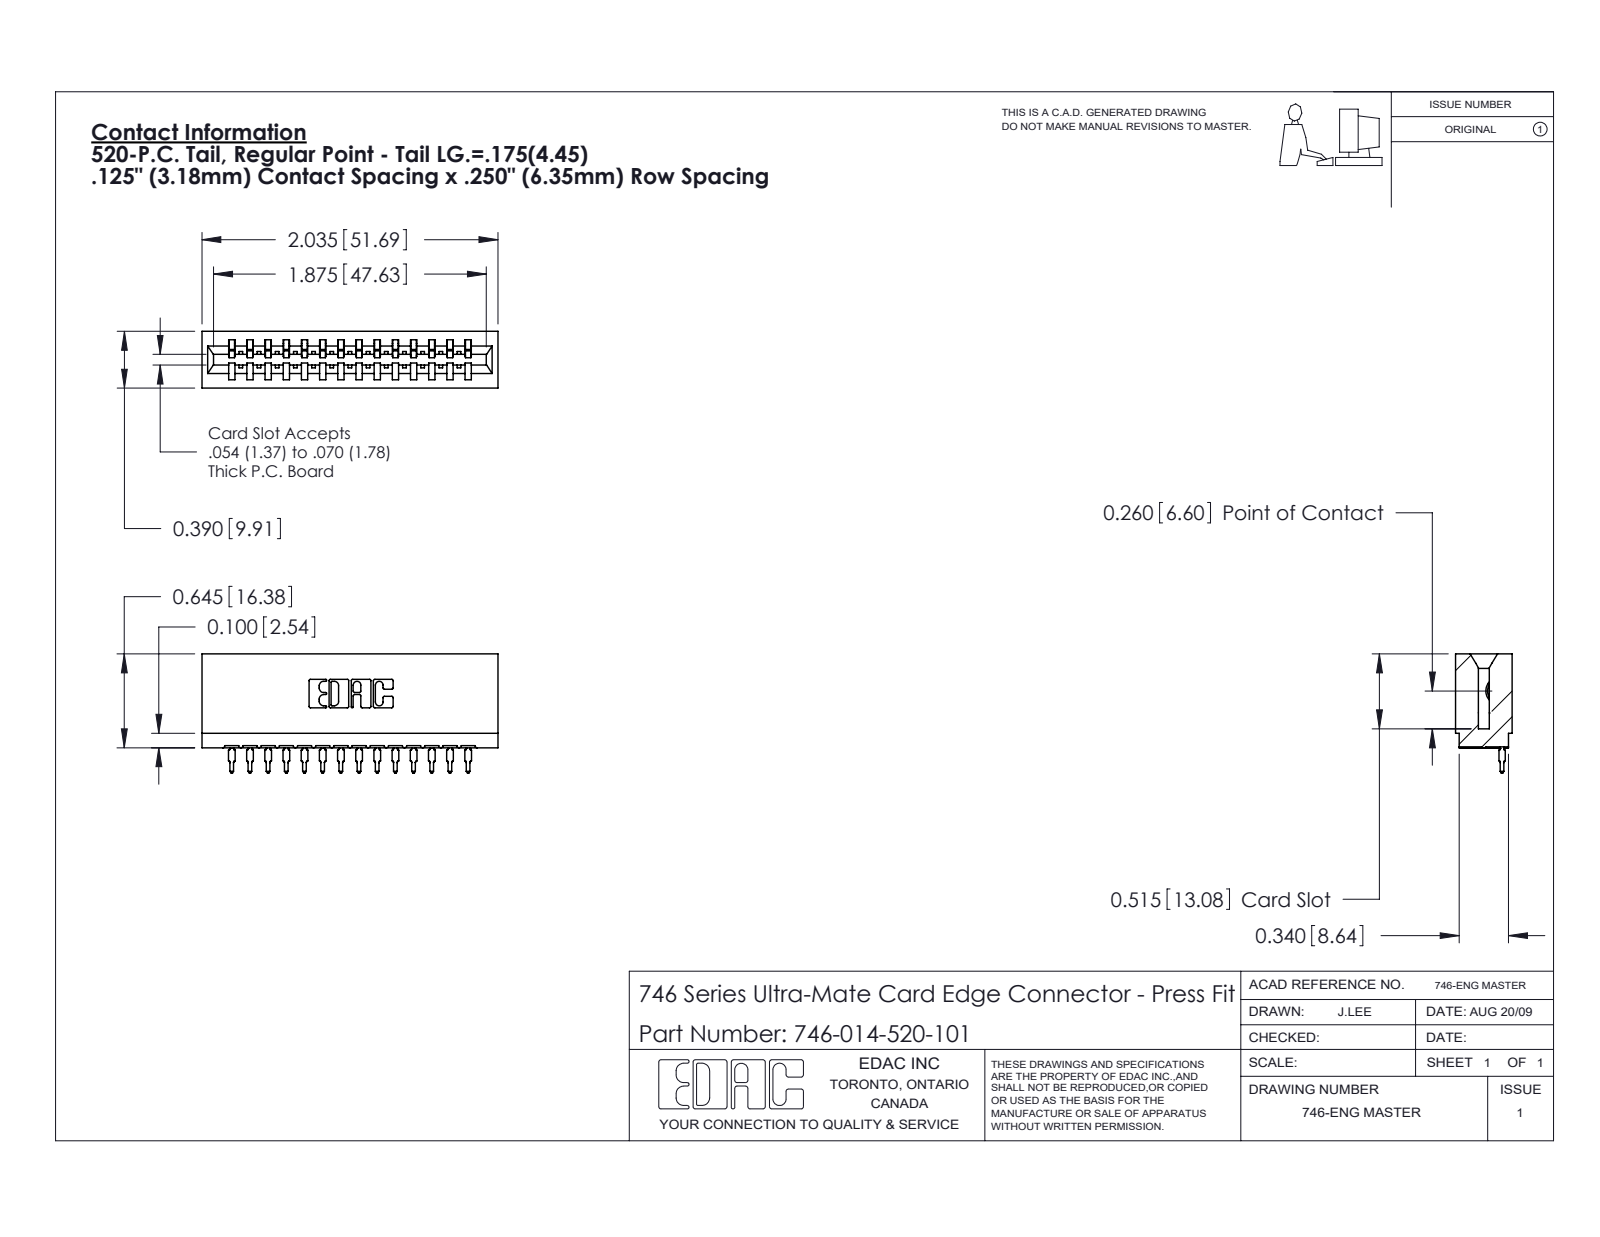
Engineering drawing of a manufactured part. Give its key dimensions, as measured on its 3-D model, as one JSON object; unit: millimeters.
{"part_name": "746-292-001_520; 746 Part_.515 Slot Depth - 01; 746-014-520-101", "step_written_by": "SolidWorks 2020 (CONFIG_CONTROL_DESIGN)", "units": "millimeters", "bodies": {"solids": 15, "faces": 1609, "planar": 937, "cylindrical": 308, "other": 364}, "overall_size": [51.7, 20.8, 9.9], "volume_mm3": 5570, "surface_area_mm2": 7690, "partial_cylinders_radius": [[0.5, 28], [0.3, 22], [0.4, 15], [0.2, 6], [0.8, 6], [0.1, 4], [0.3, 4], [0.7, 3]], "face_to_face_distances": [6.4, 8.5, 1.4, 12.7, 9.9, 1.1, 3.2, 5.3, 3.2, 7.4]}
